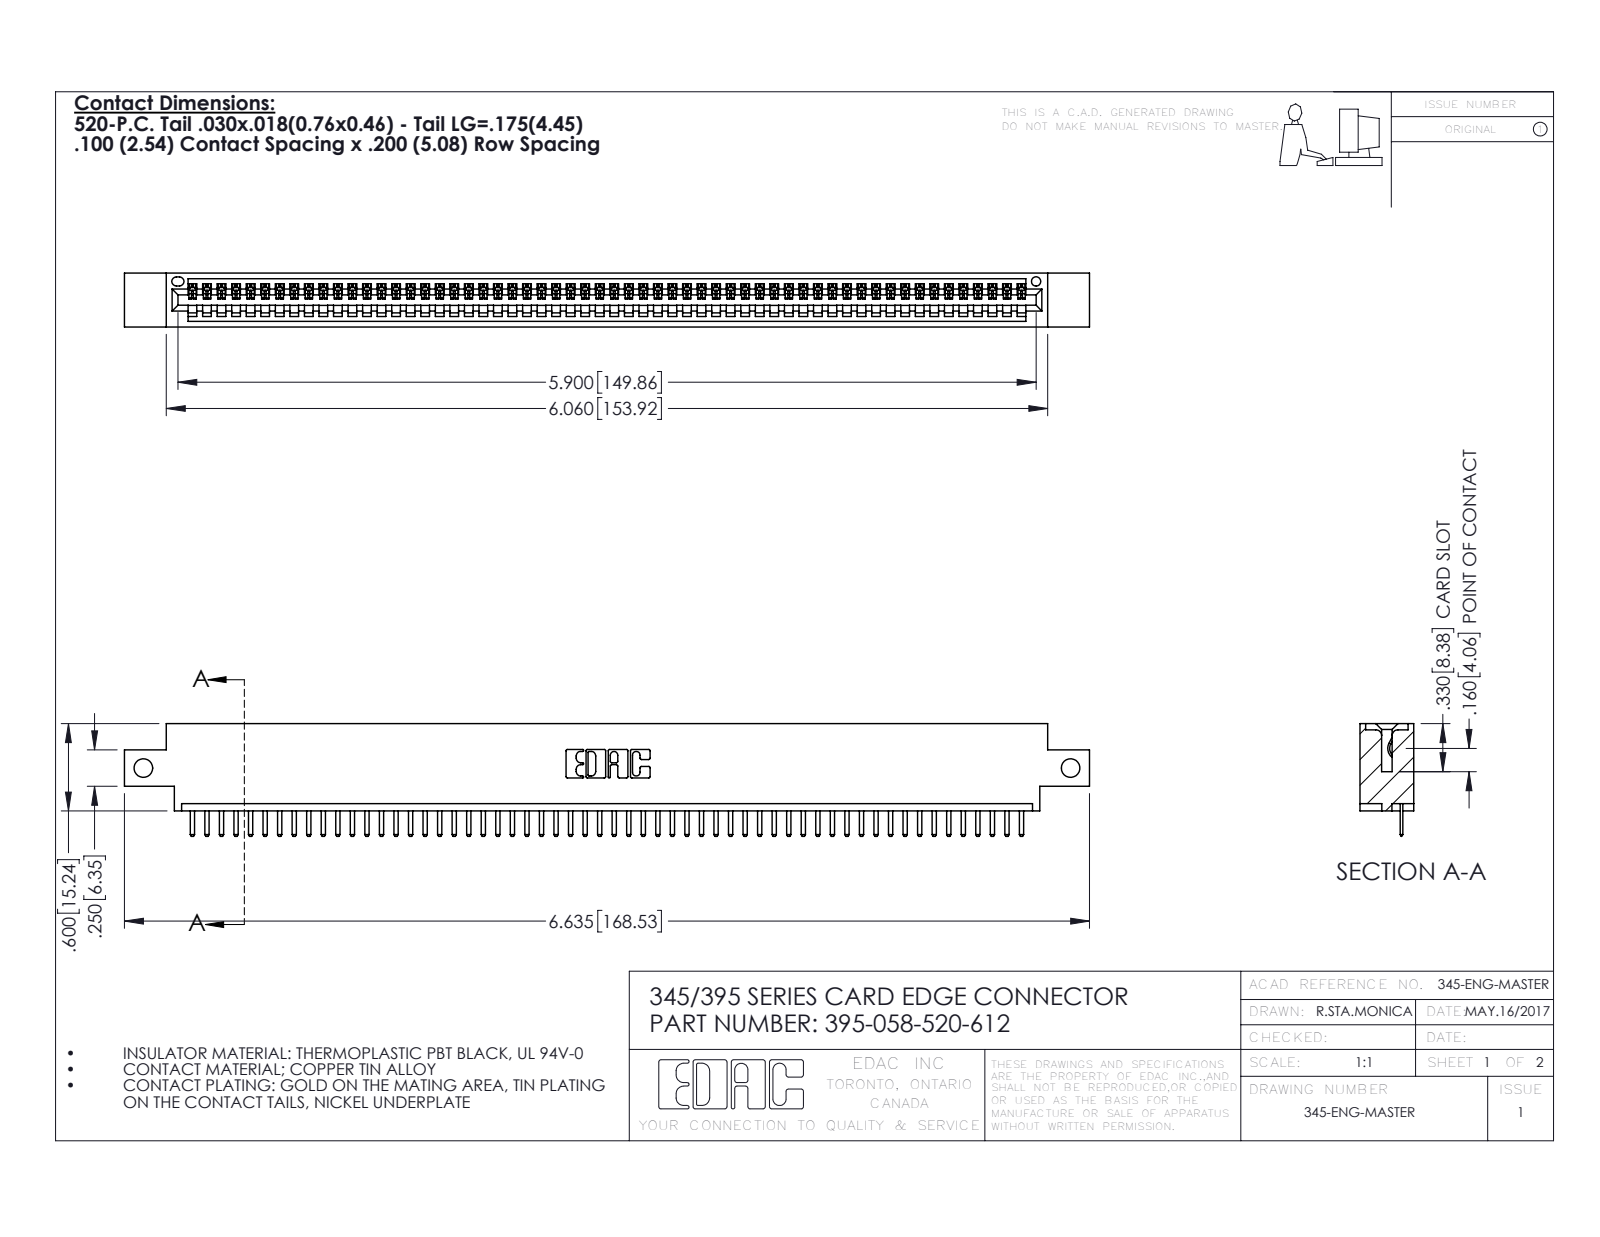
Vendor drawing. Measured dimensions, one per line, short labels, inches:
name: 395-058-520-612; 345-292-001_345-293-120; 345 Part_0.170 Offset - Side Mount
written by: SolidWorks 2016 (CONFIG_CONTROL_DESIGN)
unit: in
bodies: 59 solids, 3726 faces (2520 planar, 1206 cylindrical, 0 other)
size: 6.635 × 0.775 × 0.37
volume: 0.962 in³; area: 31.95 in²
holes: 2× ⌀0.128, 1× ⌀0.064
rounds: 118× R0.01, 116× R0.006, 22× R0.01, 6× R0.007, 6× R0.031, 3× R0.026, 2× R0.031, 2× R0.04
face distances: 0.298, 0.072, 0.37, 0.2, 0.098, 0.272, 0.025, 0.225, 0.072, 0.175
hole spacings: 6.375
